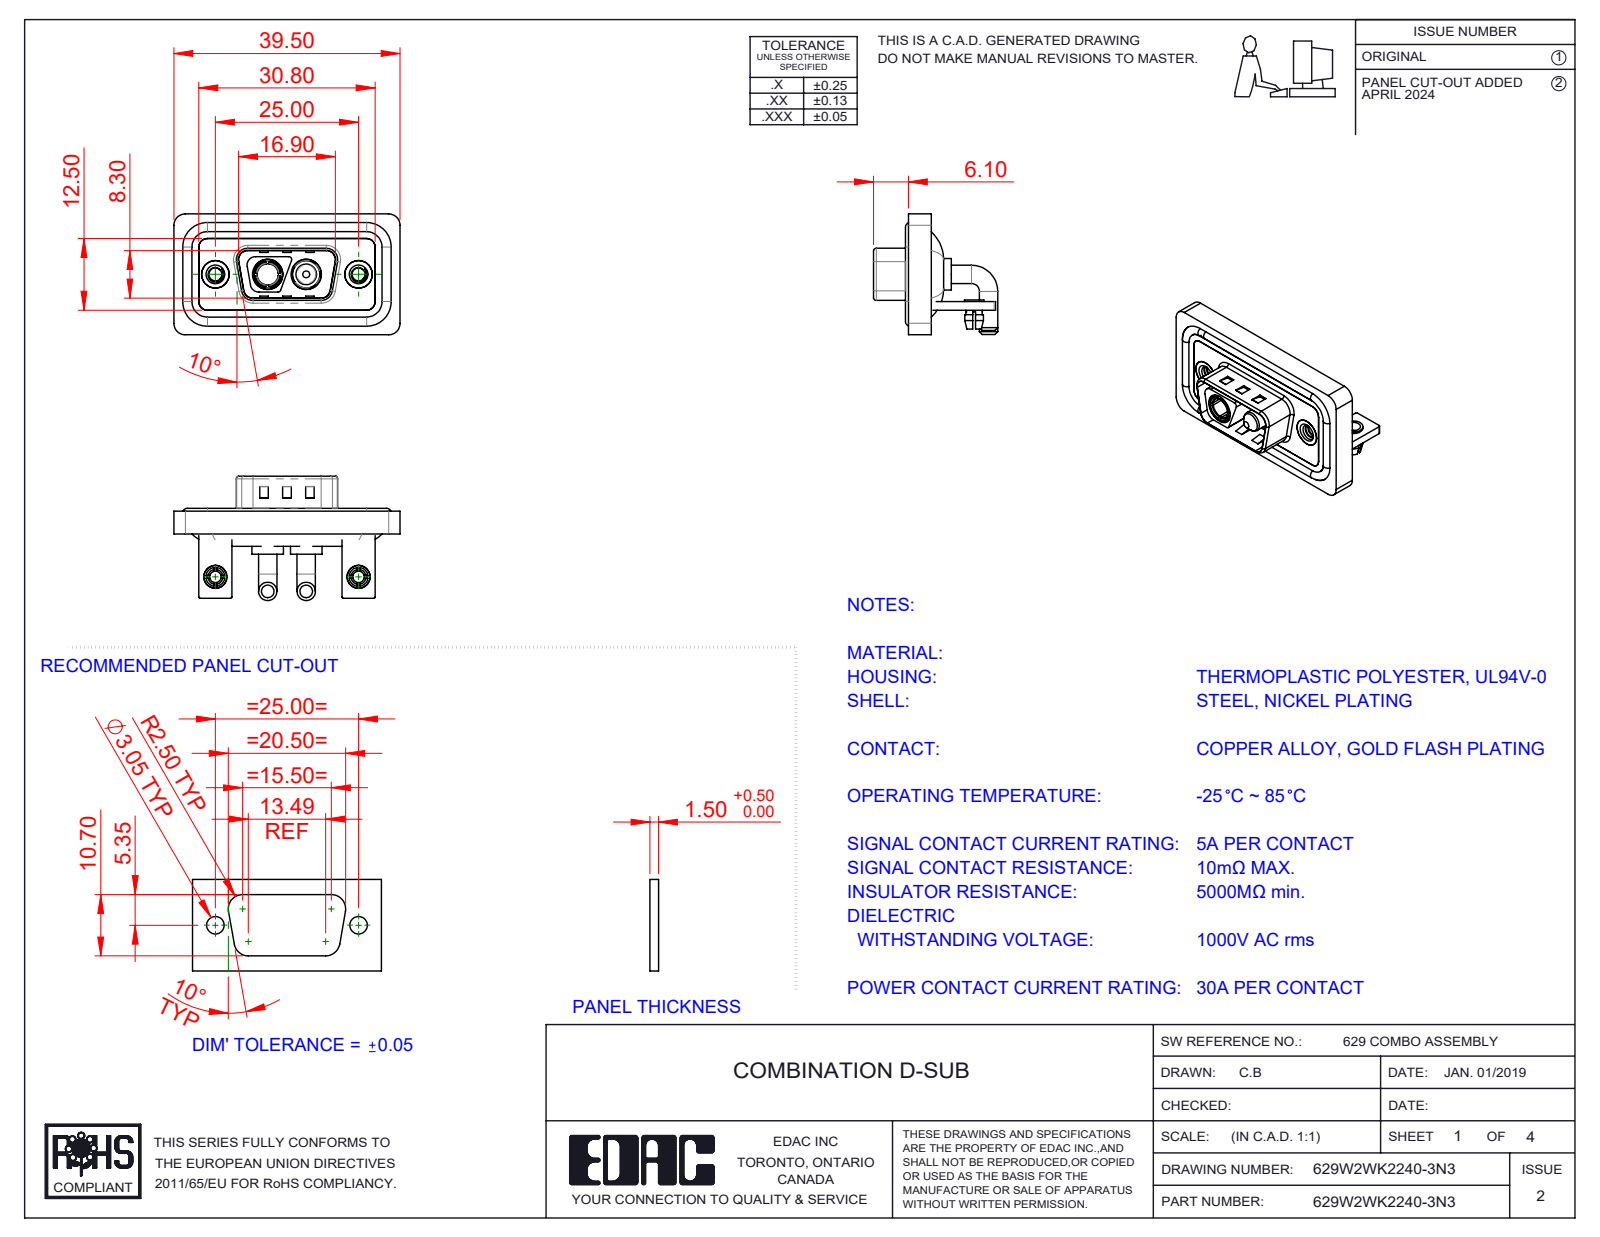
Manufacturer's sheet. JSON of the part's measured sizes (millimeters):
{"part_name": "629Combo Shell Front_09 Contacts; Power Socket_30A RA; 629W2WK2240-3N3; 629Combo Stabilizer Bracket (+6 more)", "step_written_by": "SolidWorks 2023 (CONFIG_CONTROL_DESIGN)", "units": "millimeters", "bodies": {"solids": 15, "faces": 674, "planar": 257, "cylindrical": 281, "other": 136}, "overall_size": [39.5, 21.7, 21.1], "volume_mm3": 5054, "surface_area_mm2": 8367, "round_holes": [[2, 2], [2.26, 2], [2.5, 2], [3.2, 2], [4, 2], [4.8, 2], [4.85, 2], [5, 2], [5.3, 2], [3.7, 1]], "round_bosses_or_shafts": [[3.2, 4], [1.6, 4], [5.5, 2], [5.2, 2], [4.9, 2], [4.75, 2], [4, 2], [3.75, 2]], "partial_cylinders_radius": [[1.5, 20], [2, 19], [0.25, 16], [0.5, 11], [1.6, 8], [0.6, 4], [0.65, 4], [0.9, 4]], "face_to_face_distances": [0.4, 1.5, 2.9, 0.8, 1.1, 1.2, 2.1, 1.6, 3.7, 2.5], "hole_center_spacings": [9.14, 15.86, 25, 6.72]}
